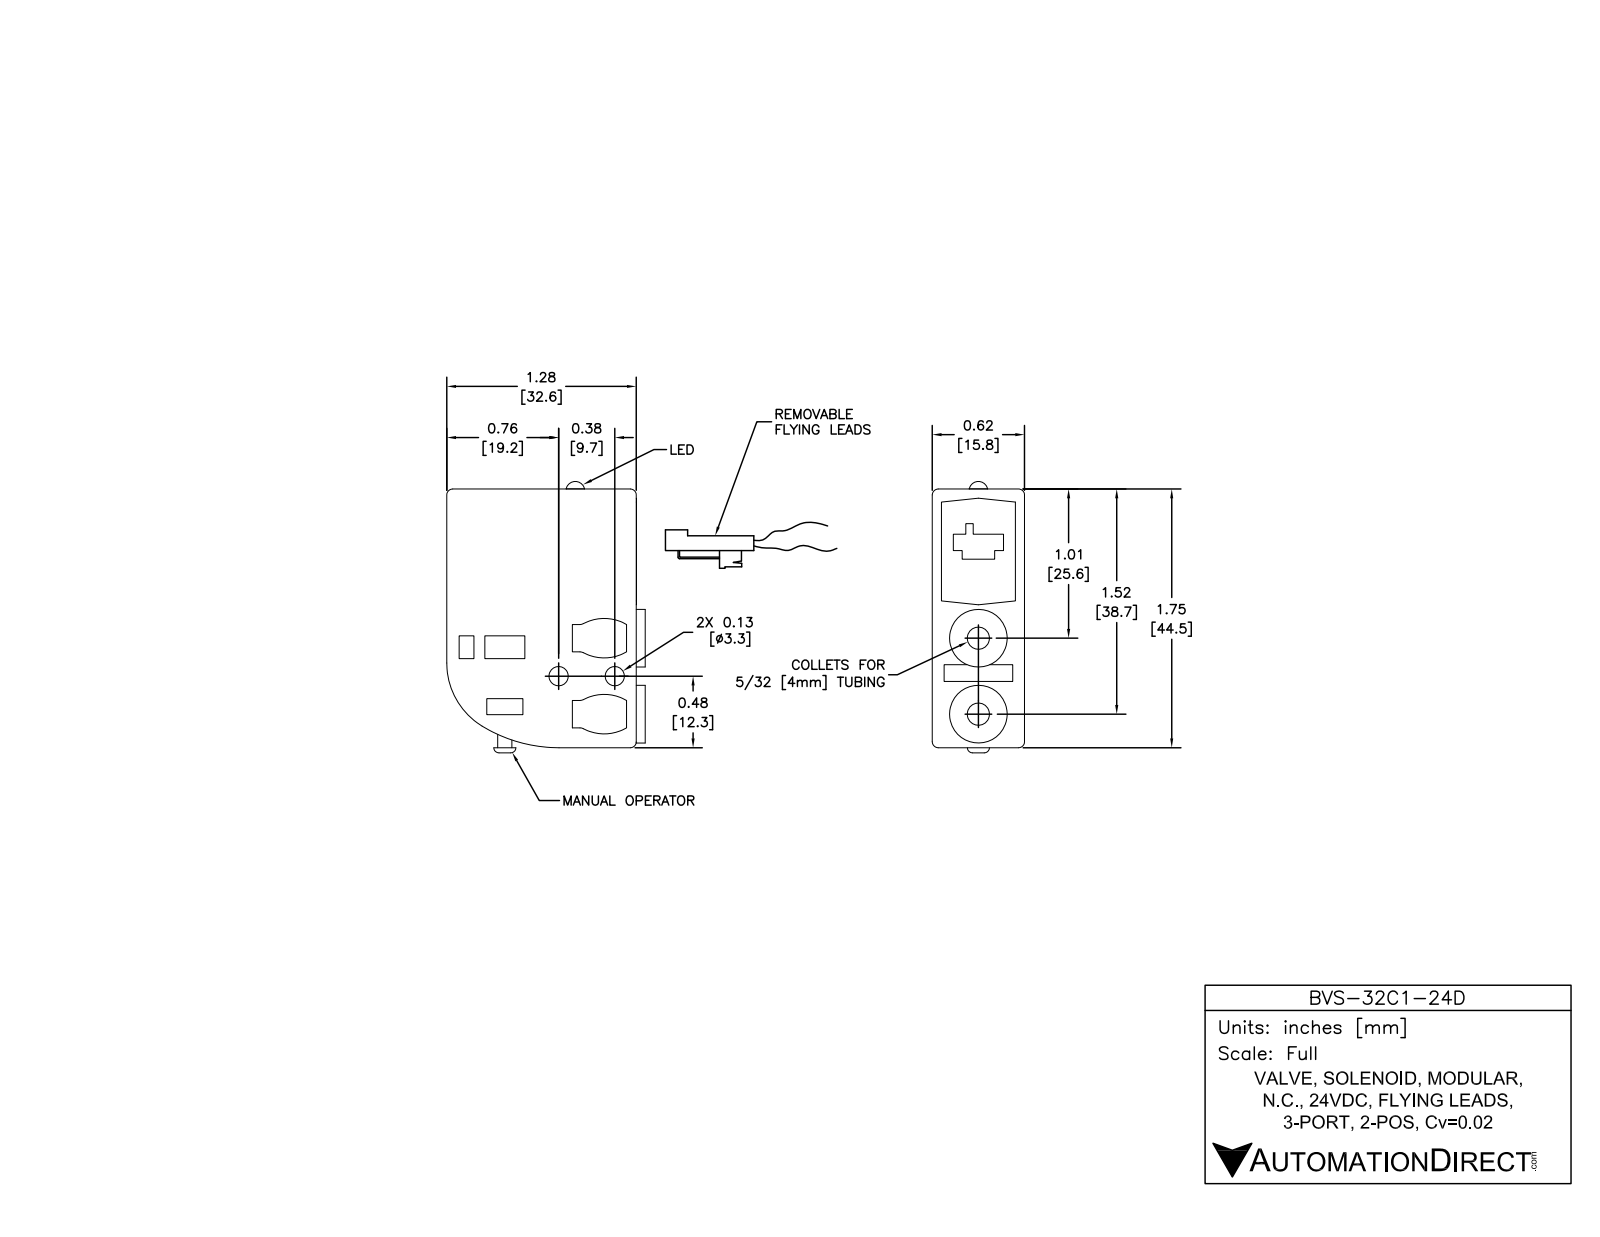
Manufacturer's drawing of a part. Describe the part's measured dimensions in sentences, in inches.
The part is named "BVS-32C1-24D". Its 3-D file was written by "SolidWorks 2013 (AUTOMOTIVE_DESIGN)". It is 1 solid with 158 faces: 93 planar, 52 cylindrical and 13 other. Overall it measures 1.836 by 1.347 by 0.624 inches. Its volume is 1.246 cubic inches and its surface area 10.17 square inches. Round holes: 2 of diameter 0.13, 2 of diameter 0.15, 2 of diameter 0.254, 1 of diameter 0.046. Round bosses or shafts: 2 of diameter 0.39, 1 of diameter 0.124, 1 of diameter 0.096. Partial cylindrical surfaces (rounded edges, fillets, slot ends): 11 of radius 0.04, 4 of radius 0.05, 4 of radius 0.3, 1 of radius 0.5, 1 of radius 1. The main face-to-face distances are 0.624, 0.1, 0.524, 1.287, 1.288, 1.75, 0.424, 0.06, 0.059, 1.347. The hole center spacings are 0.061, 0.38, 0.453, 0.514.
